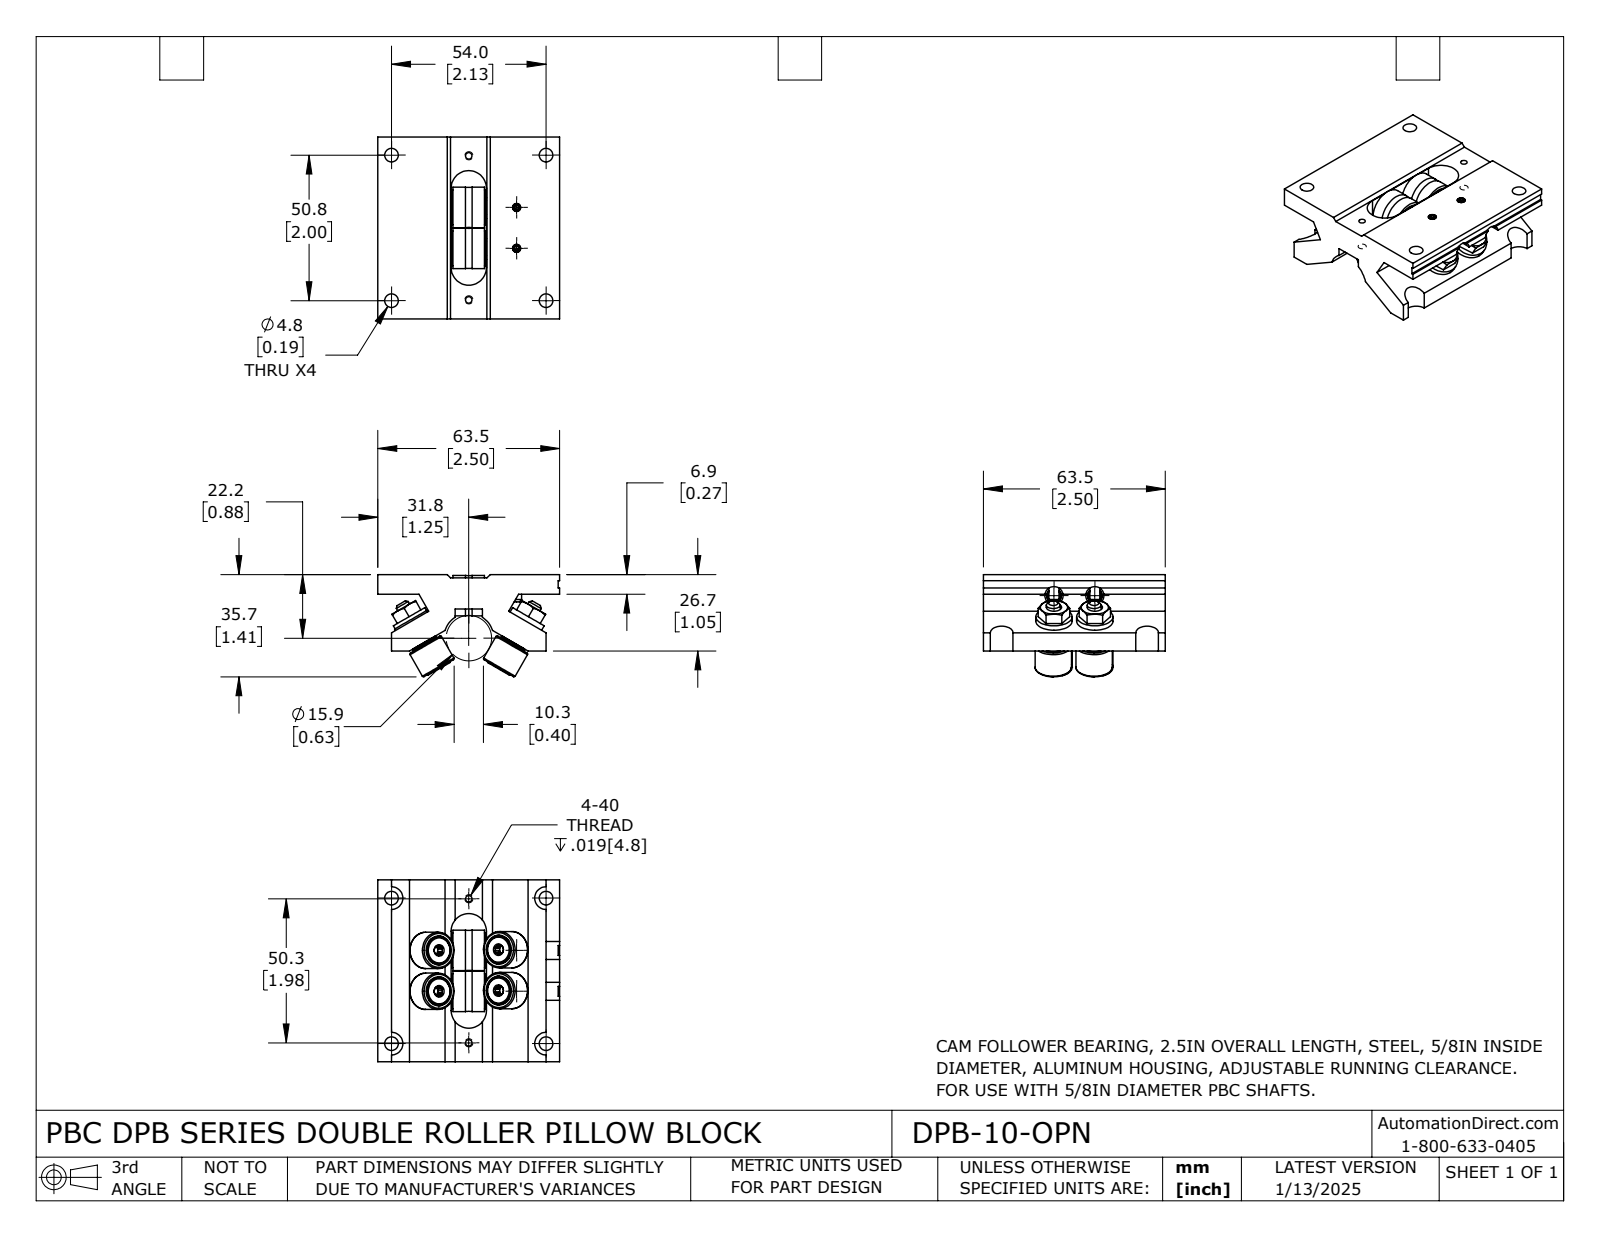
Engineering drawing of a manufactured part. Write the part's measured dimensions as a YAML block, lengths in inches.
part_name: "DPB-10-OPN"
step_written_by: "SolidWorks 2023 (CONFIG_CONTROL_DESIGN)"
units: inches
bodies: {solids: 19, faces: 574, planar: 229, cylindrical: 181, other: 164}
overall_size: [2.5, 2.5, 1.405]
volume: 3.938
surface_area: 43.68
round_holes:
  - {diameter: 0.129, count: 4}
  - {diameter: 0.149, count: 4}
  - {diameter: 0.187, count: 4}
  - {diameter: 0.399, count: 4}
  - {diameter: 0.089, count: 2}
  - {diameter: 0.107, count: 2}
  - {diameter: 0.156, count: 2}
  - {diameter: 0.19, count: 2}
  - {diameter: 0.193, count: 2}
  - {diameter: 0.196, count: 2}
  - {diameter: 0.197, count: 2}
  - {diameter: 0.2, count: 2}
round_bosses_or_shafts:
  - {diameter: 0.5, count: 6}
  - {diameter: 0.369, count: 4}
  - {diameter: 0.557, count: 2}
  - {diameter: 0.515, count: 2}
  - {diameter: 0.478, count: 2}
  - {diameter: 0.25, count: 2}
  - {diameter: 0.2, count: 2}
  - {diameter: 0.197, count: 2}
partial_cylinders:
  - {radius: 0.156, count: 4}
  - {radius: 0.242, count: 1}
  - {radius: 0.243, count: 1}
  - {radius: 0.344, count: 1}
face_to_face_distances: [0.34, 0.27, 2.5, 0.78, 1.05, 1.493, 1.007, 0.82, 1.305, 0.187]
hole_center_spacings: [0.562, 1.063, 2.256, 0.825, 0.967, 1.344, 1.431, 1.864]
